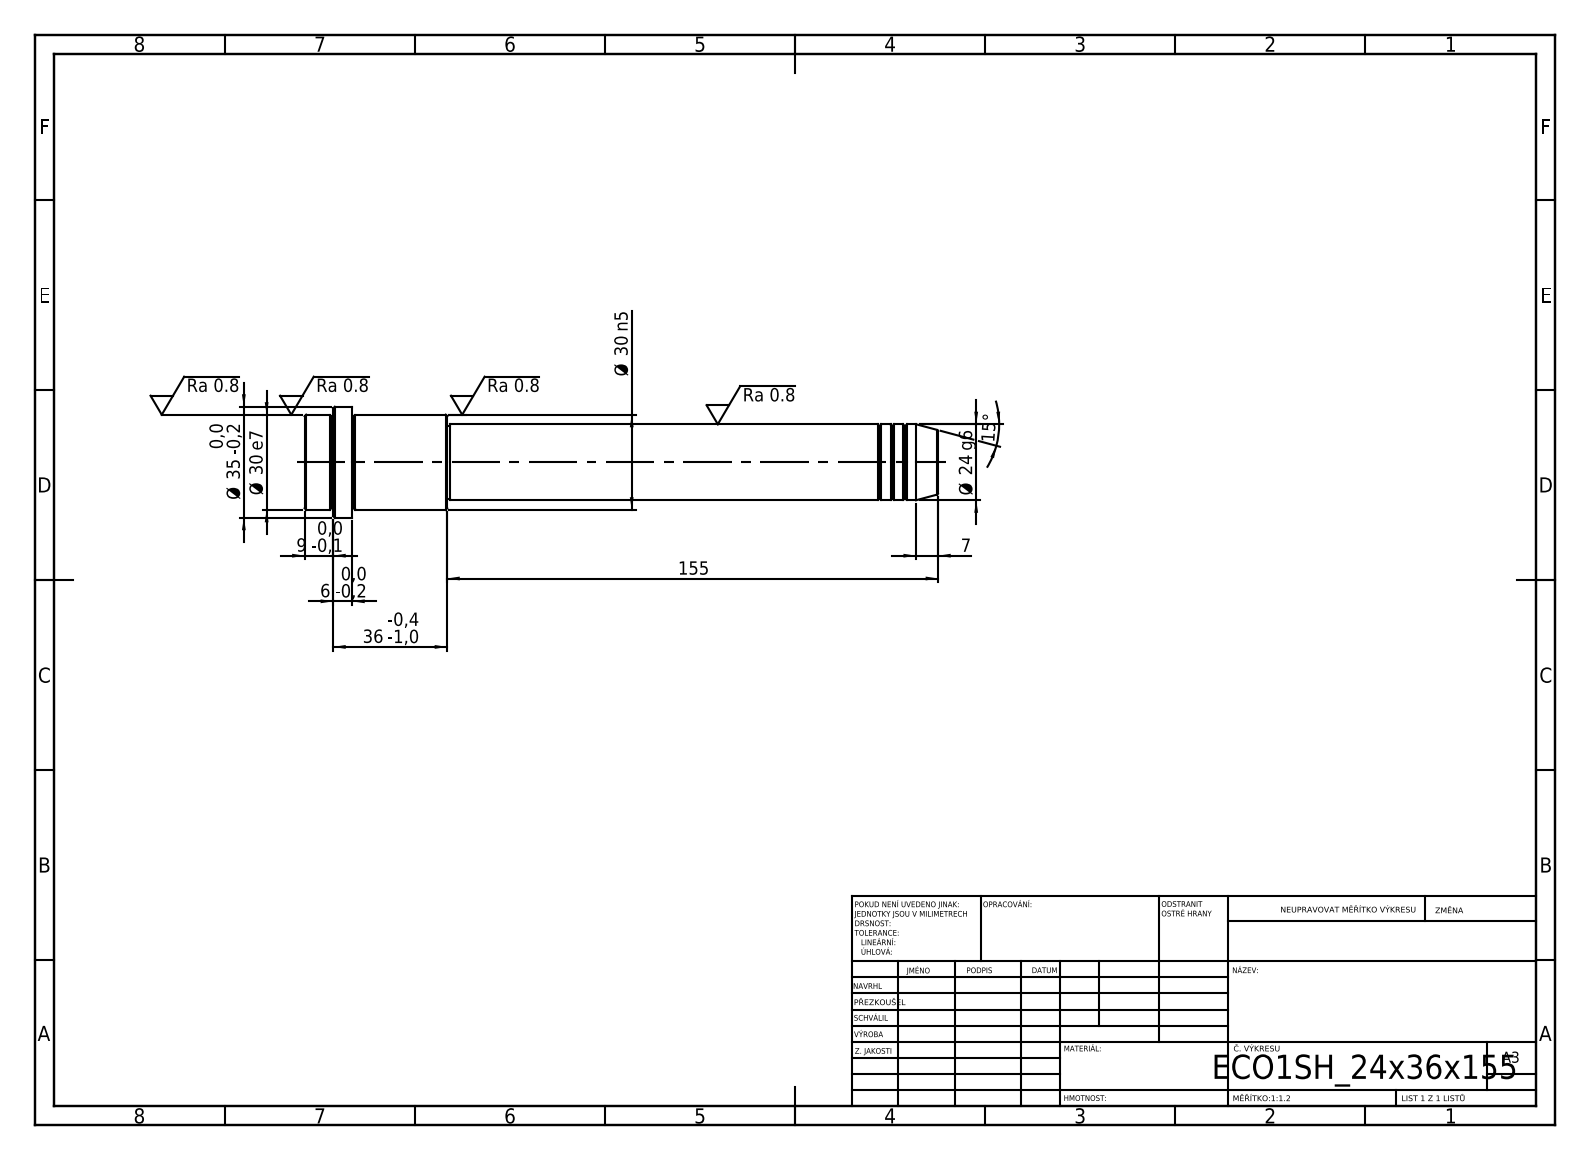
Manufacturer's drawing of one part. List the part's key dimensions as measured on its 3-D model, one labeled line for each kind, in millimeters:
STEP written by: SolidWorks 2019 (CONFIG_CONTROL_DESIGN)
Units: millimetres
Bodies: 1 solid, 52 faces (6 planar, 16 cylindrical, 30 other)
Overall size (bounding box): 200 × 35 × 35
Volume: 102 755 mm³ · Surface area: 17 988 mm²
Round bosses / shafts (diameter × count): ⌀35 ×1, ⌀30 ×1, ⌀24 ×1, ⌀23 ×1
Main face-to-face distances: 200, 185, 15, 155, 30, 45, 191, 36, 6, 9
